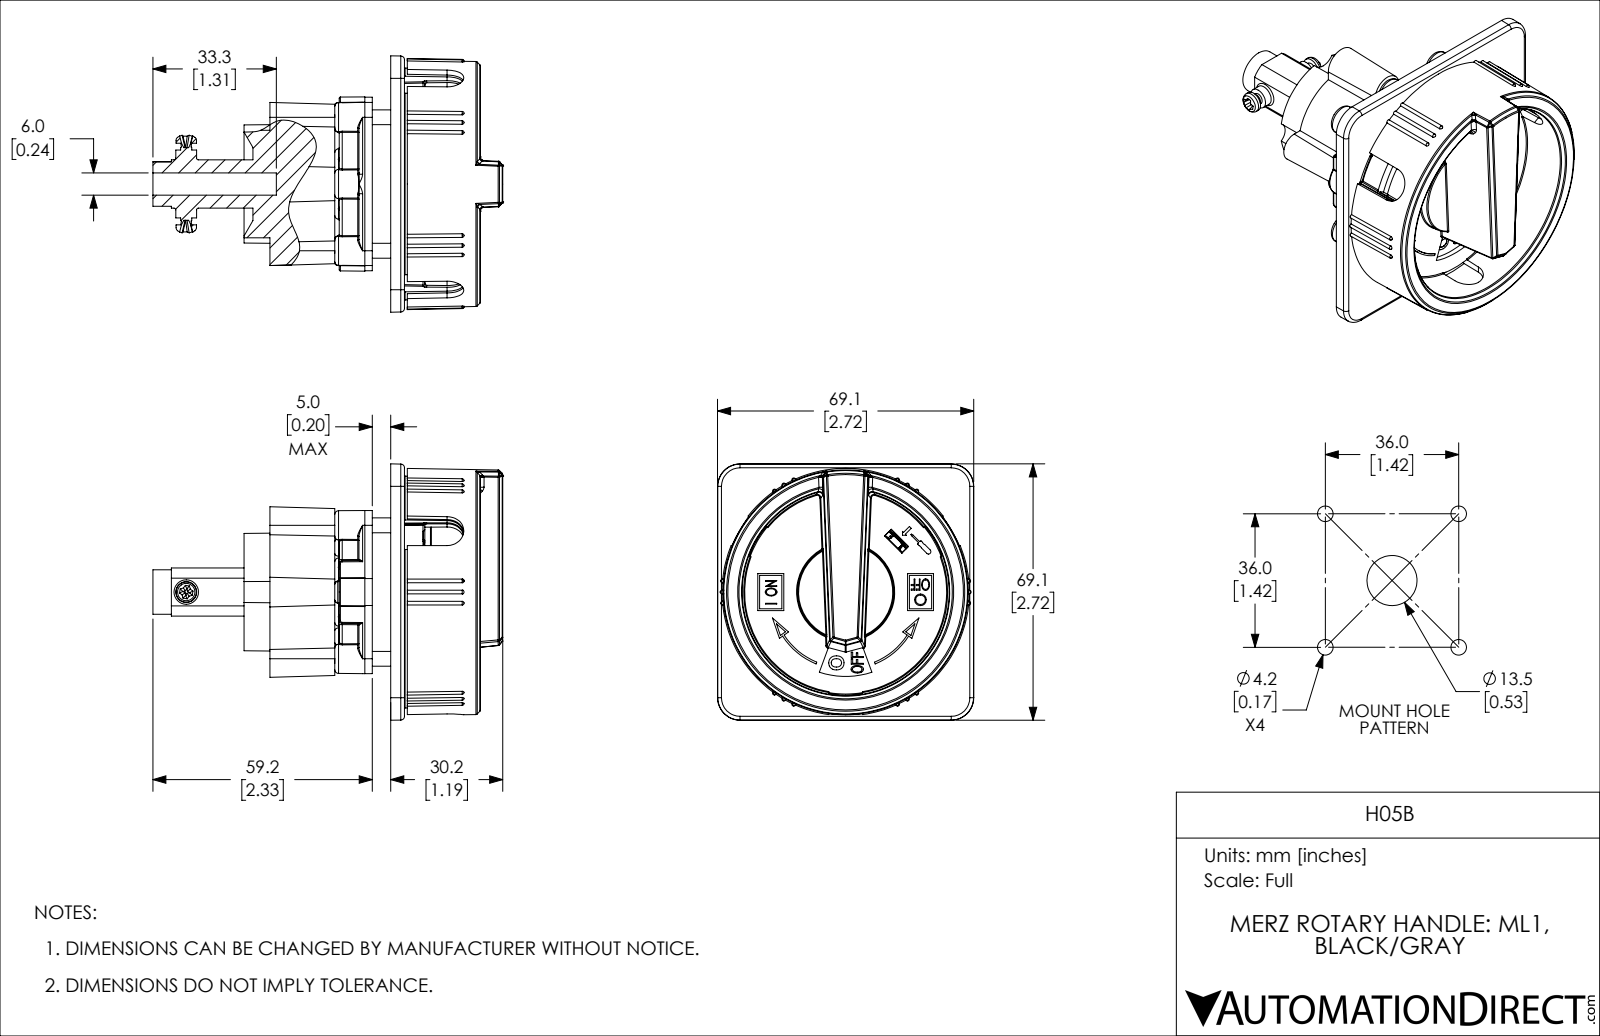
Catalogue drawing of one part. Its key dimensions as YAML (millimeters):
part_name: "H05B"
step_written_by: "SolidWorks 2019 (AUTOMOTIVE_DESIGN)"
units: millimeters
bodies: {solids: 1, faces: 2308, planar: 487, cylindrical: 417, other: 1404}
overall_size: [94.4, 69.13, 69.13]
volume: 72261
surface_area: 54937
round_bosses_or_shafts:
  - {diameter: 5, count: 6}
  - {diameter: 4, count: 4}
  - {diameter: 26, count: 1}
  - {diameter: 12, count: 1}
  - {diameter: 6, count: 1}
  - {diameter: 5.6, count: 1}
  - {diameter: 5.5, count: 1}
  - {diameter: 3, count: 1}
partial_cylinders:
  - {radius: 0.5, count: 110}
  - {radius: 0.3, count: 44}
  - {radius: 0.8, count: 22}
  - {radius: 1, count: 22}
  - {radius: 0.25, count: 15}
  - {radius: 0.2, count: 8}
  - {radius: 0.9, count: 6}
  - {radius: 4, count: 6}
face_to_face_distances: [1.5, 5, 3.5, 0.5, 2, 7, 5.5, 14.2, 8.7, 9.2]
